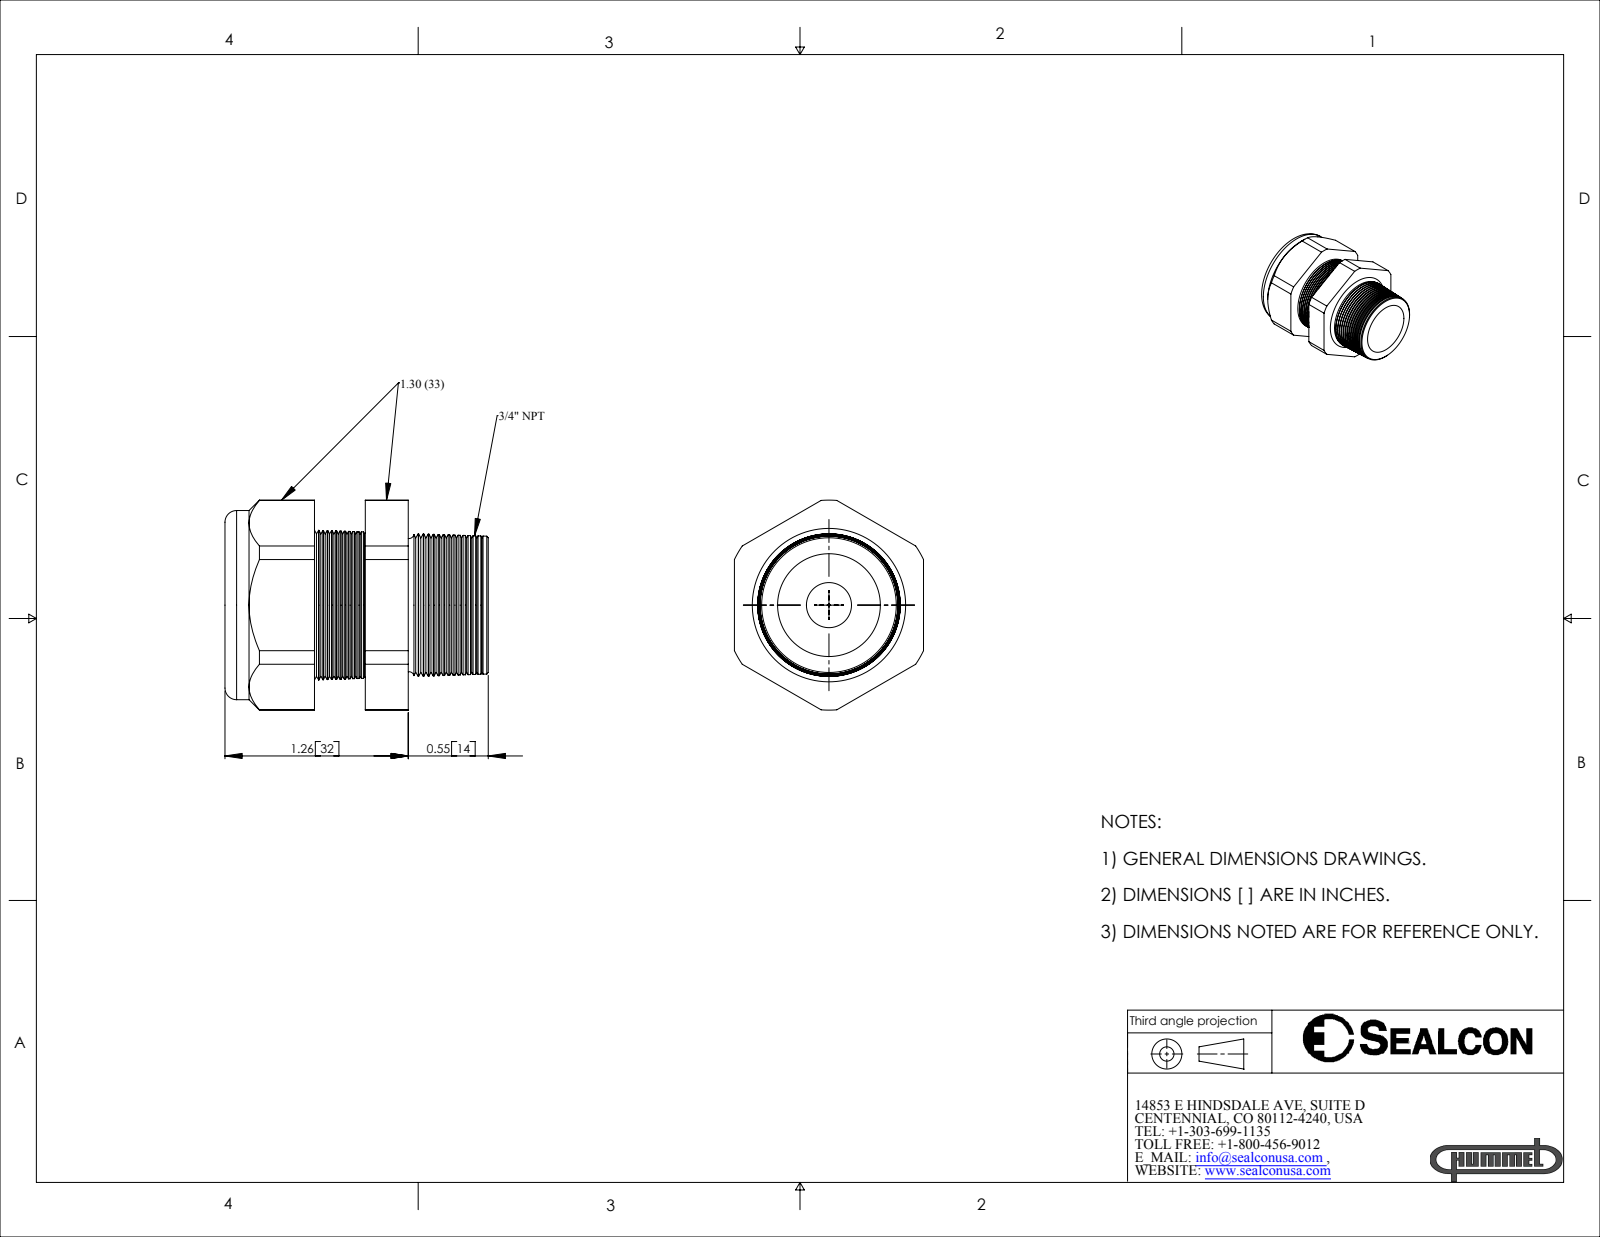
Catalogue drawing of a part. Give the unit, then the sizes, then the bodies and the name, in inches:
Units: inches
Overall size (bounding box): 1.81 × 1.443 × 1.3
Round holes (diameter × count): ⌀0.31 ×1, ⌀0.69 ×1, ⌀0.71 ×1
Round bosses / shafts (diameter × count): ⌀1.3 ×1
Partial cylindrical surfaces — rounded edges, fillets, slot ends (radius × count): R0.721 ×1
Main face-to-face distances: 1.3, 0.965, 0.615, 0.35, 1.26, 0.645, 0.295, 0.35, 0.265, 0.615
Volume: 1.343 in³ · Surface area: 18.27 in²
Bodies: 2 solids, 226 faces (20 planar, 22 cylindrical, 184 other)
Part name (STEP PRODUCT): CD21N5-BK
STEP written by: SolidWorks 2007 (CONFIG_CONTROL_DESIGN)
